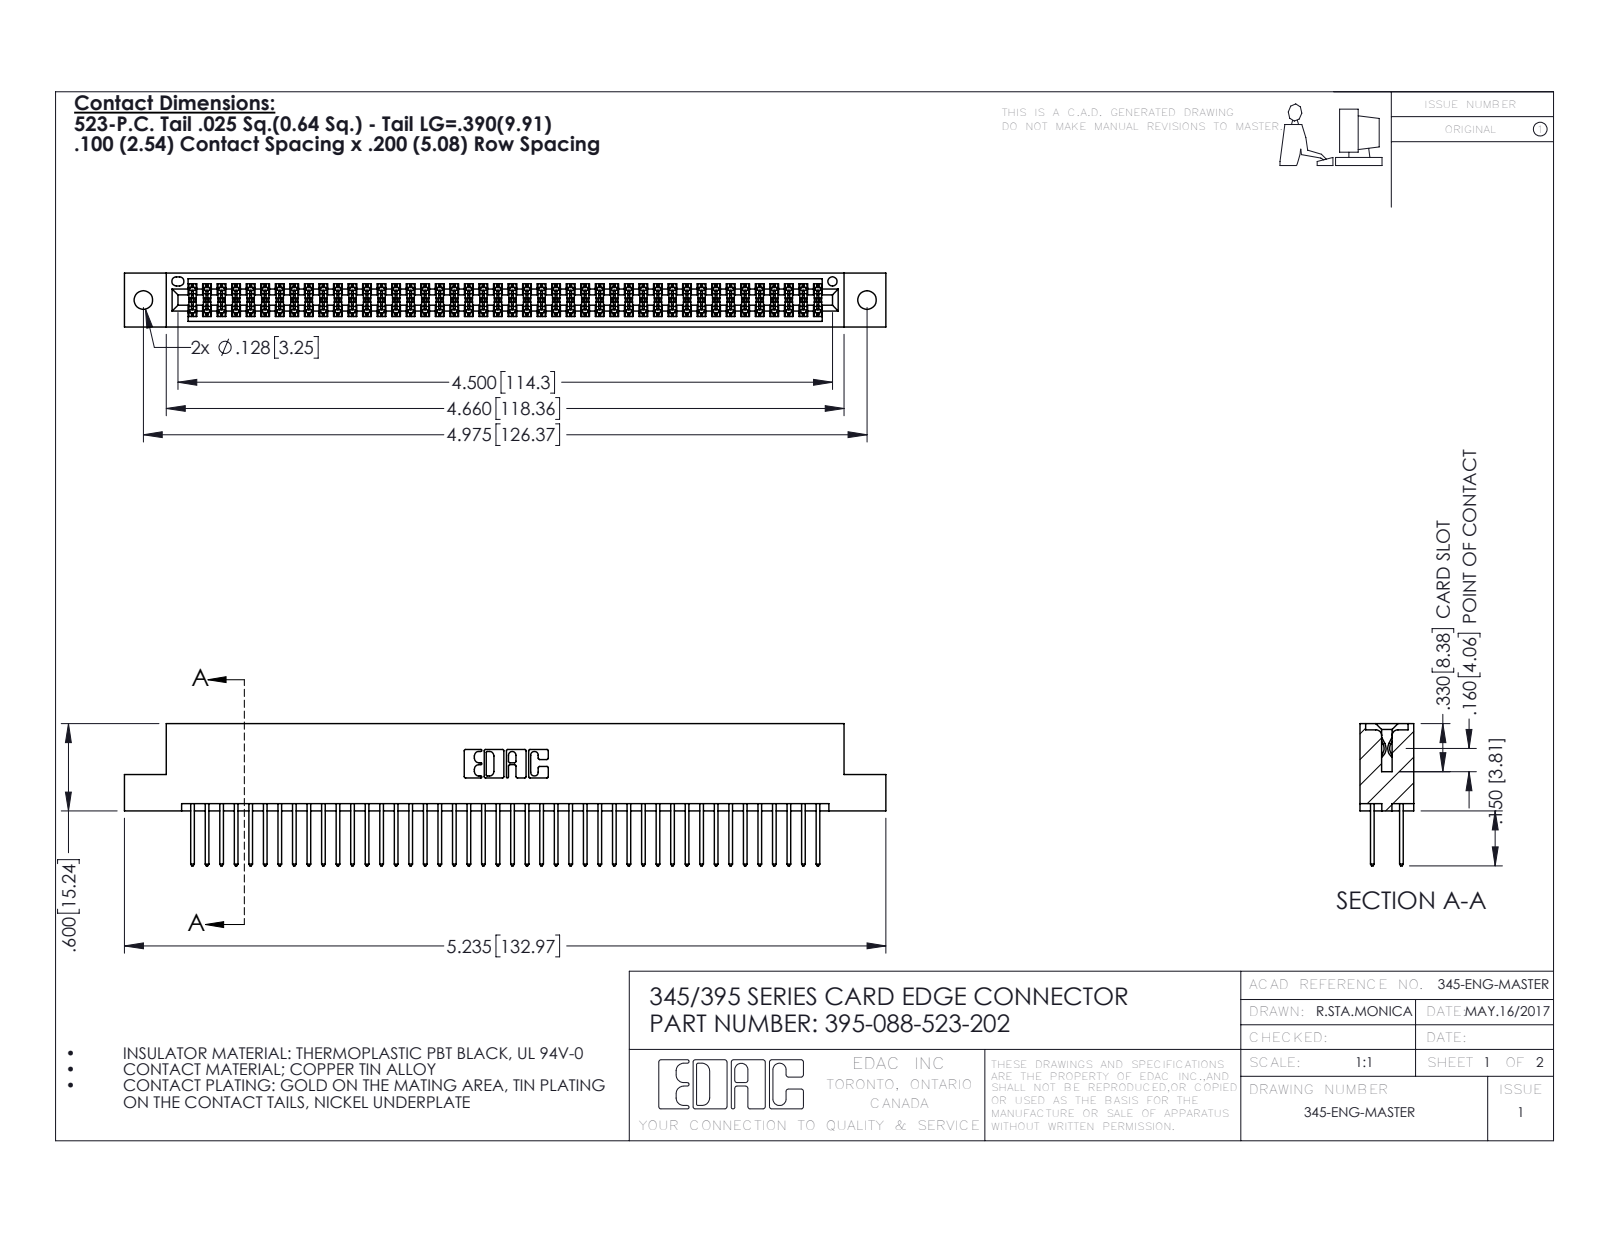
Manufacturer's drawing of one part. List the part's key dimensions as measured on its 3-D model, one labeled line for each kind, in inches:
Part name (STEP PRODUCT): 345-292-001_345-293-123; 345 Part_Flush Mounting Lugs - 0.128 Dia; 395-088-523-202
STEP written by: SolidWorks 2016 (CONFIG_CONTROL_DESIGN)
Units: inches
Bodies: 89 solids, 4526 faces (2984 planar, 1542 cylindrical, 0 other)
Overall size (bounding box): 5.235 × 0.977 × 0.37
Volume: 0.798 in³ · Surface area: 30.86 in²
Round holes (diameter × count): ⌀0.128 ×2, ⌀0.064 ×1
Partial cylindrical surfaces — rounded edges, fillets, slot ends (radius × count): R0.006 ×132, R0.01 ×88, R0.01 ×22, R0.007 ×6, R0.031 ×6, R0.026 ×3, R0.014 ×2, R0.019 ×2
Main face-to-face distances: 0.298, 0.072, 0.2, 0.098, 0.272, 0.025, 0.37, 0.225, 0.175, 0.149
Hole centre spacings: 0.27, 4.739, 4.975
